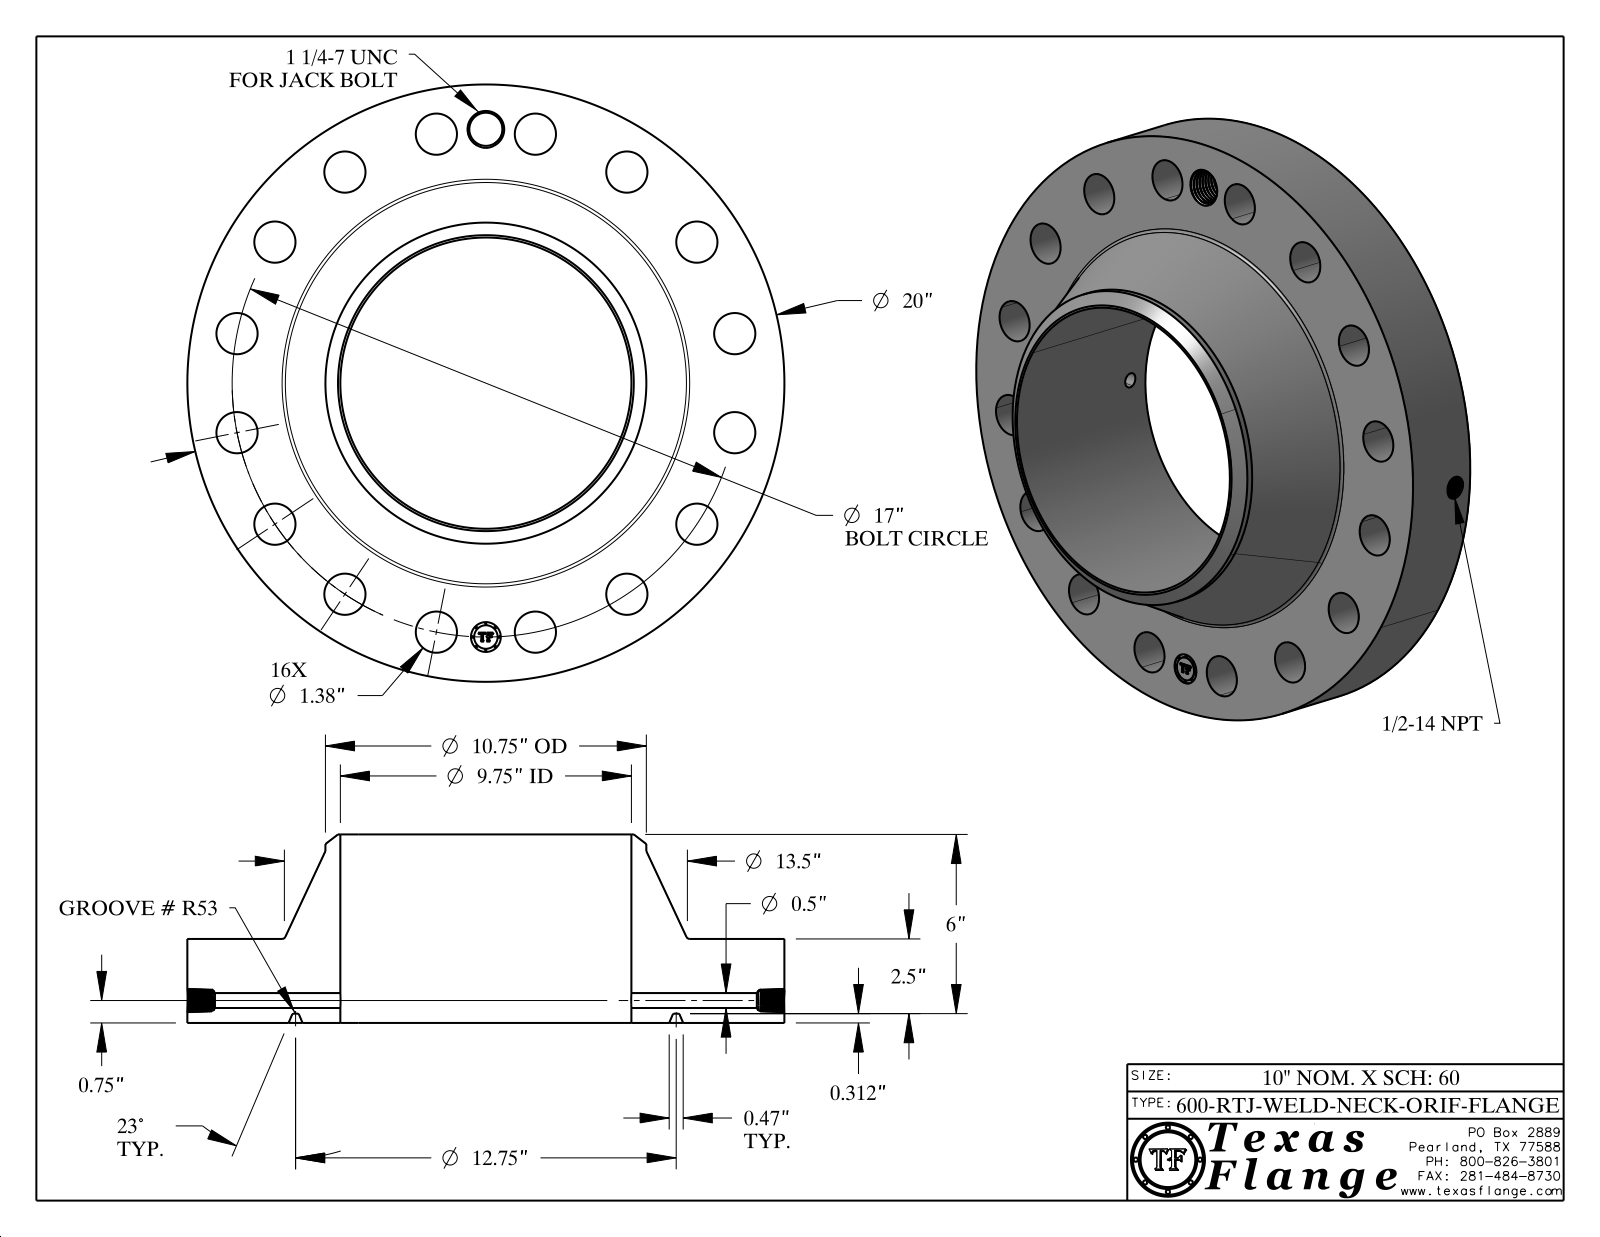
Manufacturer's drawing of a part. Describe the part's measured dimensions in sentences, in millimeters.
The part is named "600-RTJ-WELD-NECK". Its 3-D file was written by "CATIA V5 STEP AP214 (AUTOMOTIVE_DESIGN)". It is 1 solid with 822 faces: 370 planar, 117 cylindrical and 335 other. Overall it measures 508 by 508 by 160.3 millimeters. Its volume is 11 880 000 cubic millimeters and its surface area 727 100 square millimeters. Round holes: 16 of diameter 35.1, 1 of diameter 12.7, 1 of diameter 17.1, 1 of diameter 25.4, 1 of diameter 28.2, 1 of diameter 247.7. Round bosses or shafts: 8 of diameter 1.5, 1 of diameter 508, 1 of diameter 273.1, 1 of diameter 20. The main face-to-face distances are 71.4, 7.9, 63.5, 160.3, 152.4, 88.9, 71, 63.1, 0.4, 89.3. The hole center spacings are 215.9, 305.3, 398.9, 423.5, 84.3, 239.9, 359, 431.8.
